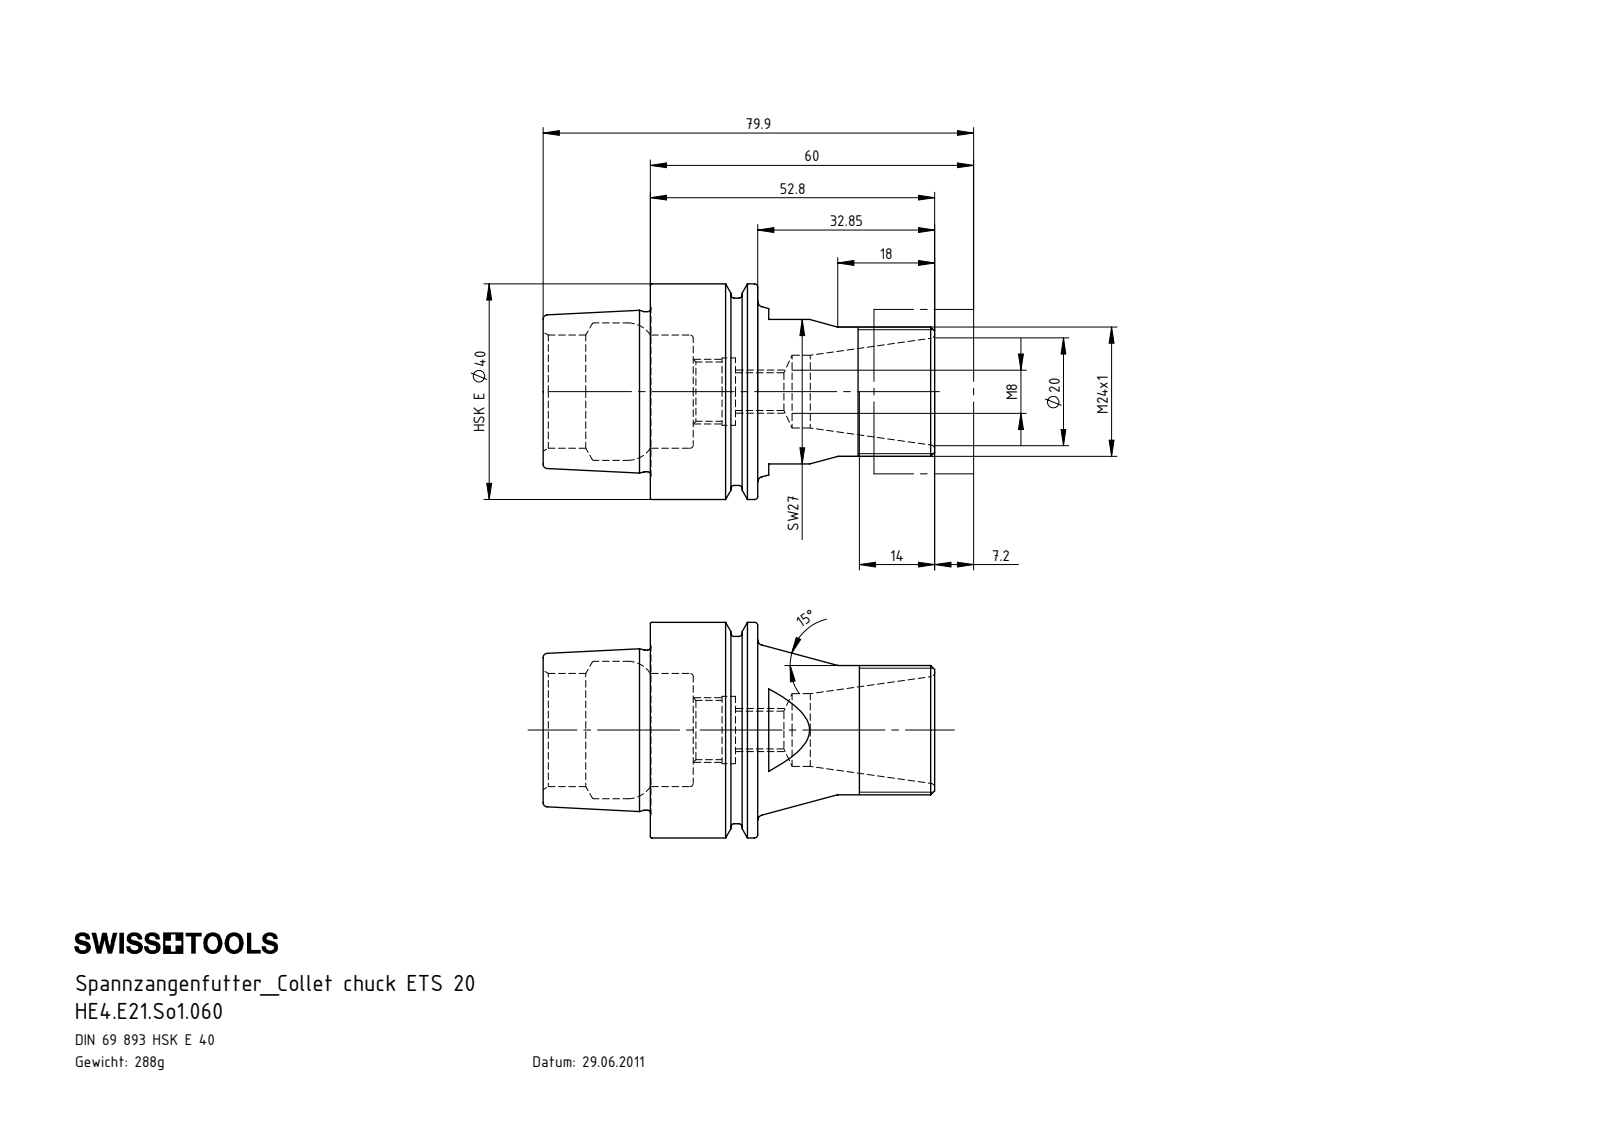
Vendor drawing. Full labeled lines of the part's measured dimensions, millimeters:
Part name (STEP PRODUCT): HE4-E21.So1.060; HE4-E21.So1.060_B_Fertigbearbeitung
STEP written by: SolidWorks 2015 (AUTOMOTIVE_DESIGN)
Units: millimetres
Bodies: 1 solid, 87 faces (13 planar, 24 cylindrical, 50 other)
Overall size (bounding box): 72.7 × 40 × 40
Volume: 35 908 mm³ · Surface area: 13 259 mm²
Round holes (diameter × count): ⌀7 ×1, ⌀11 ×1, ⌀12.5 ×1, ⌀13.5 ×1, ⌀21 ×1, ⌀25.5 ×1
Round bosses / shafts (diameter × count): ⌀40 ×1, ⌀34.75 ×1, ⌀29.71 ×1, ⌀24 ×1
Main face-to-face distances: 19.95, 7.95, 12, 19.9, 27.85, 39.85, 35.7, 15.8, 7.85, 4.15
